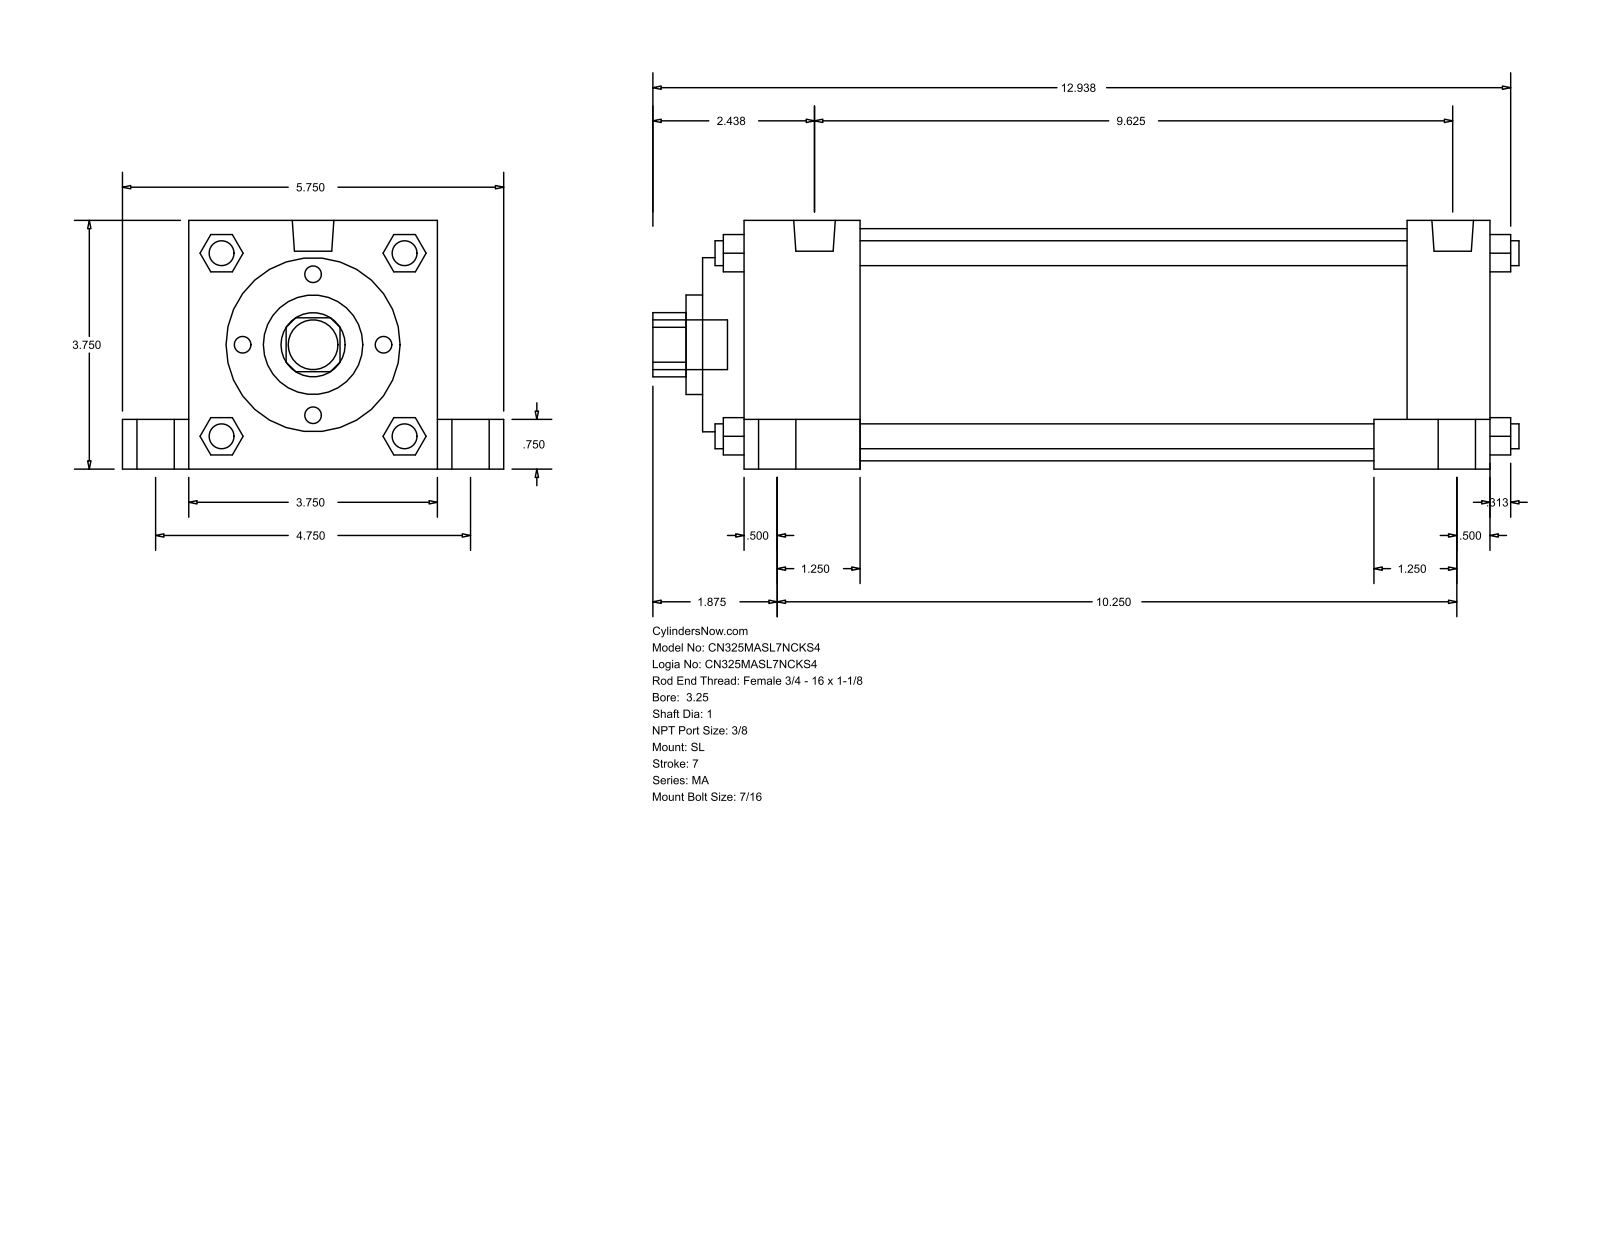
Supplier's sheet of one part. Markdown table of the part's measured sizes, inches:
| quantity | value |
| --- | --- |
| part name | MA_SL__0325_1 |
| STEP written by | GSSL Pune (CONFIG_CONTROL_DESIGN) |
| units | inches |
| bodies | 0 solids, 150 faces (113 planar, 37 cylindrical, 0 other) |
| overall size | 13.063 × 5.75 × 3.75 |
| round holes (diameter × count) | 1 × 1, 1.5 × 1, 2.625 × 1, 3.5 × 1 |
| round bosses / shafts (diameter × count) | 0.813 × 4, 0.563 × 4, 0.437 × 4, 0.375 × 4, 0.627 × 2, 0.75 × 1 |
| partial cylindrical surfaces (radius × count) | 0.484 × 1 |
| main face-to-face distances | 3.75, 11.25, 8.25, 0.625, 1, 4.75, 0.75, 10, 1.25, 1.75 |
